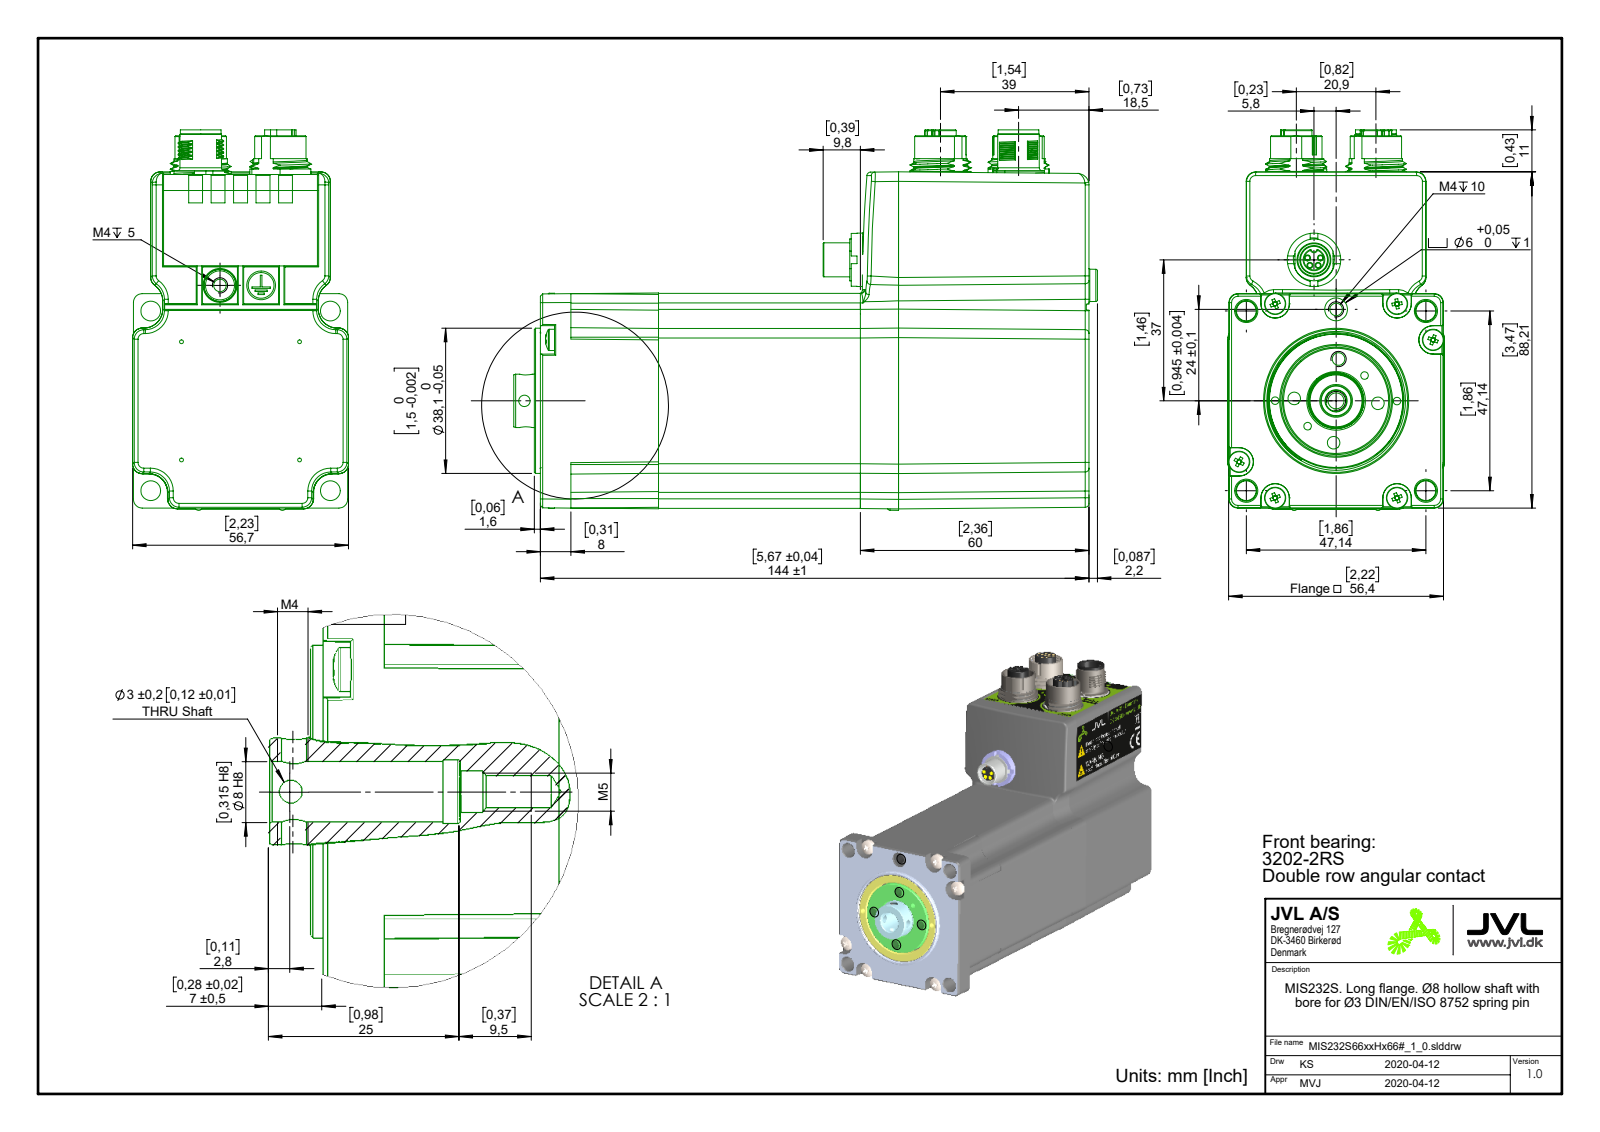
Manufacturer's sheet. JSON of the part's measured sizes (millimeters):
{"part_name": "MIS232S66xxHx66#_1_0", "step_written_by": "SolidWorks 2018 (AUTOMOTIVE_DESIGN)", "units": "millimeters", "bodies": {"solids": 2, "faces": 2199, "planar": 951, "cylindrical": 547, "other": 701}, "overall_size": [153.2, 99.83, 56.67], "volume_mm3": 501540, "surface_area_mm2": 58061, "round_holes": [[1, 31], [3.3, 7], [1.2, 4], [2, 4], [12.2, 3], [11.13, 2], [3, 1], [4.2, 1], [5.5, 1], [6, 1], [6.76, 1], [7.1, 1]], "round_bosses_or_shafts": [[5.6, 6], [3, 6], [1, 5], [1.6, 4], [0.8, 4], [13.5, 3], [16, 2], [14, 2]], "partial_cylinders_radius": [[0.2, 54], [2.5, 29], [0.1, 20], [0.3, 16], [1, 15], [5, 14], [0.8, 13], [2.3, 4]], "face_to_face_distances": [56.4, 57.23, 4.75, 52.48, 144, 88.68, 51.92, 0.56, 0.5, 4], "hole_center_spacings": [3.54, 1.63, 2.5, 3.25, 1.85, 4.94, 1.64, 2.83]}
